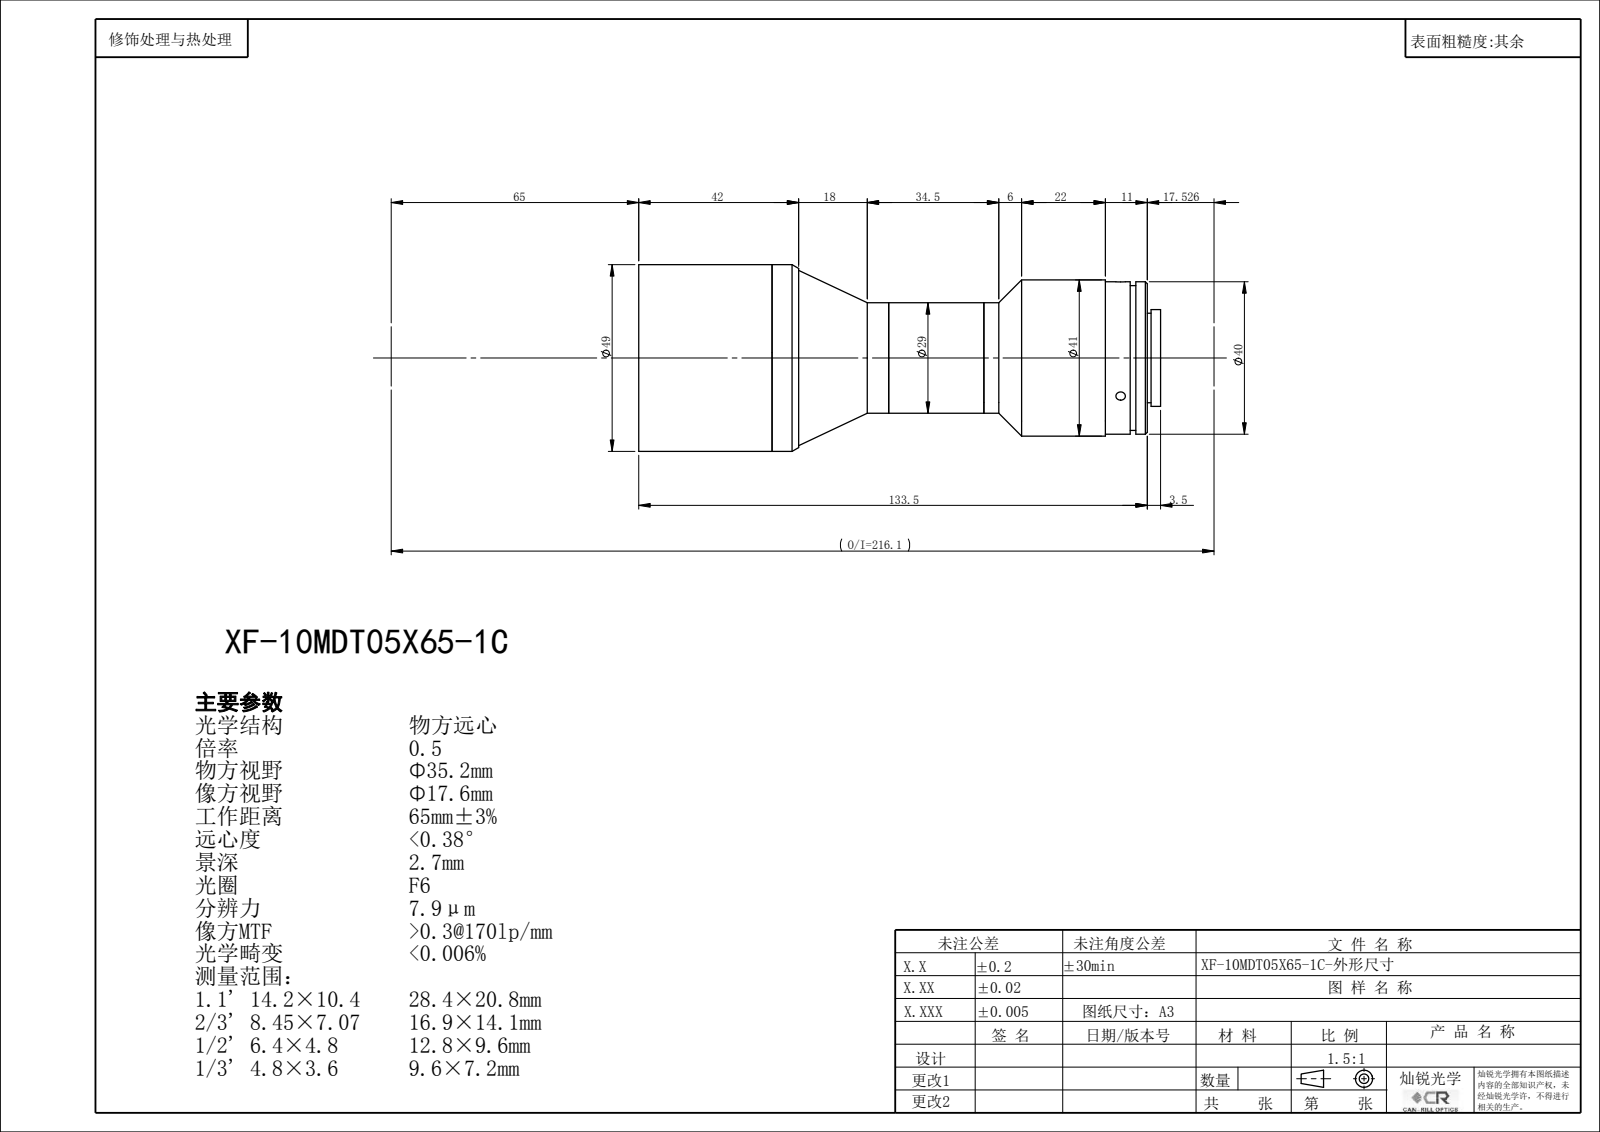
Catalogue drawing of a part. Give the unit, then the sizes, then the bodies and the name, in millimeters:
Units: millimetres
Overall size (bounding box): 137.04 × 49 × 49
Round holes (diameter × count): ⌀2.5 ×3, ⌀19 ×1, ⌀21.4 ×1, ⌀43 ×1, ⌀45.4 ×1, ⌀46 ×1
Round bosses / shafts (diameter × count): ⌀49 ×1, ⌀41 ×1, ⌀40 ×1, ⌀38 ×1, ⌀29 ×1, ⌀25.4 ×1, ⌀23.5 ×1
Main face-to-face distances: 11, 87.54, 98.54, 96.54, 9, 2, 35, 122.54, 131.54, 133.54
Bodies: 0 solids, 74 faces (22 planar, 40 cylindrical, 12 other)
Part name (STEP PRODUCT): XF-5MDT05X65-1C
STEP written by: SolidWorks 2014 (CONFIG_CONTROL_DESIGN)
